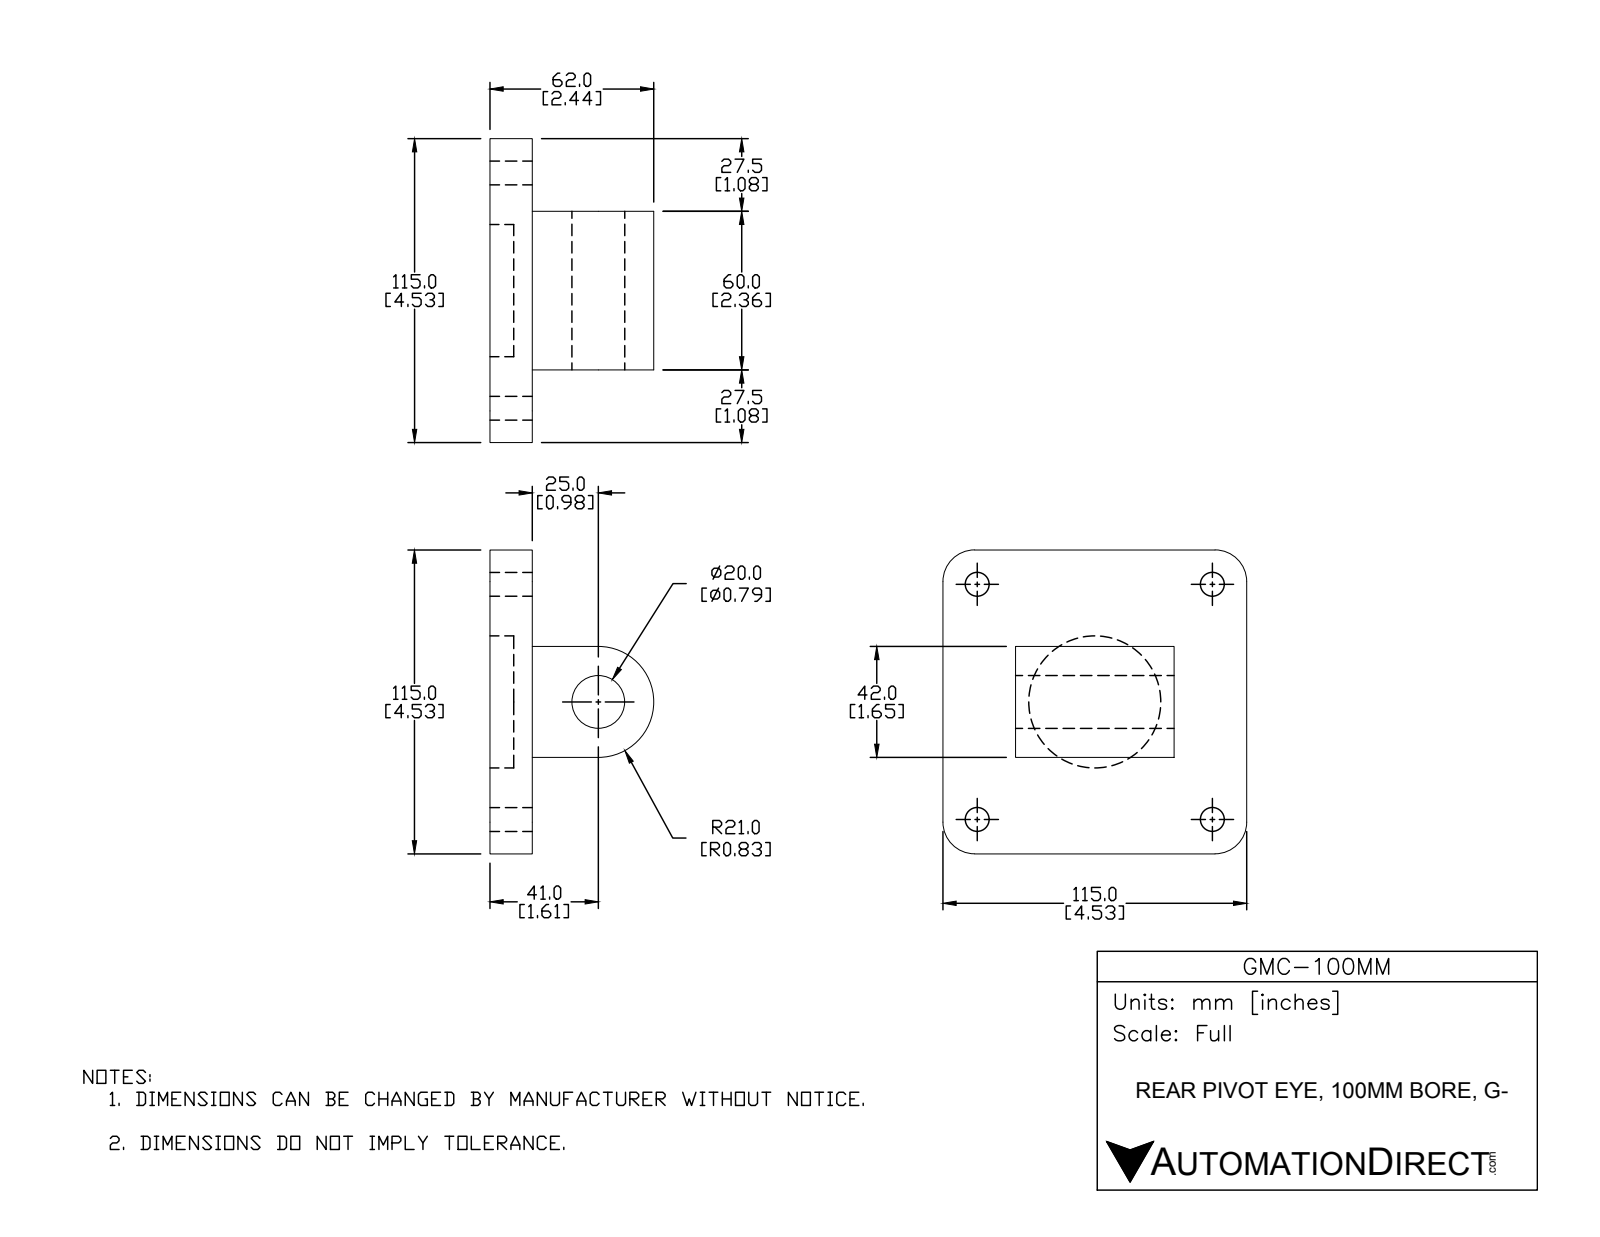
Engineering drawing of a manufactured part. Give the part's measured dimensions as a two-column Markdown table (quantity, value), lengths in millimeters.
| quantity | value |
| --- | --- |
| part name | GMC-100MM |
| STEP written by | SolidWorks 2017 (AUTOMOTIVE_DESIGN) |
| units | millimeters |
| bodies | 1 solid, 28 faces (11 planar, 17 cylindrical, 0 other) |
| overall size | 115 × 115 × 62 |
| volume | 273 593 mm³ |
| surface area | 47 013 mm² |
| round holes (diameter × count) | 9 × 4, 20 × 1, 50 × 1 |
| partial cylindrical surfaces (radius × count) | 12 × 4, 21 × 1 |
| main face-to-face distances | 16, 36.5, 78.5, 115, 27.5, 87.5, 9, 7, 42, 60 |
| hole center spacings | 62.93, 89, 125.87 |
